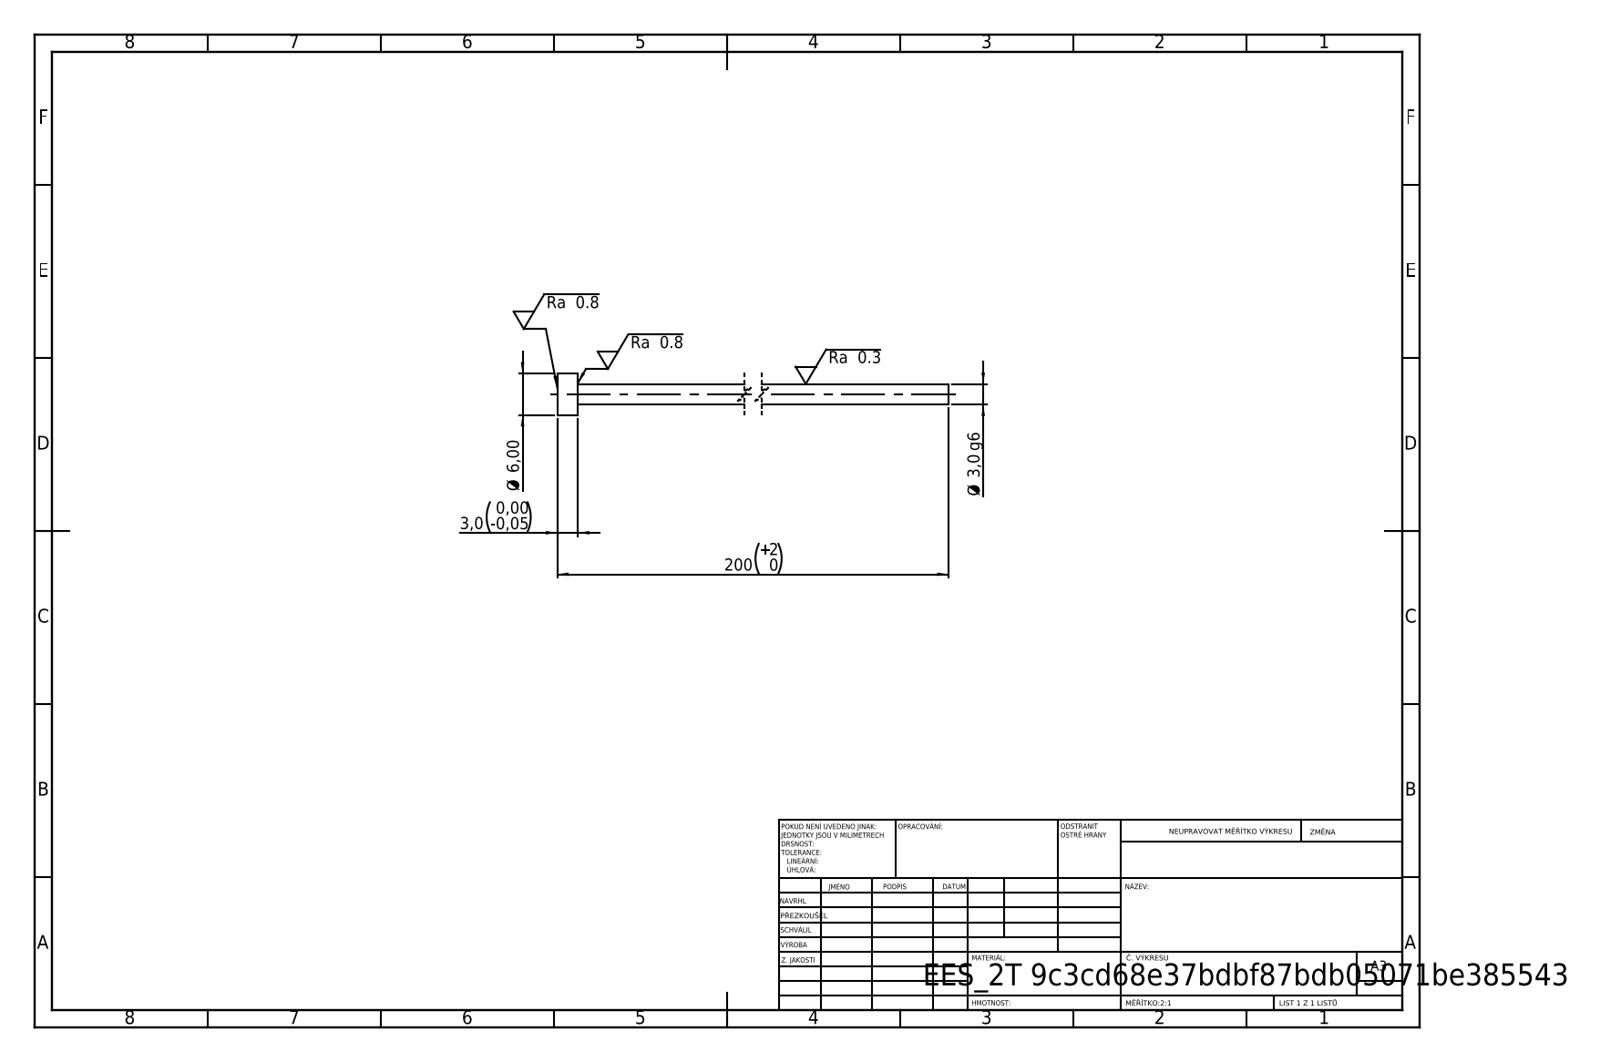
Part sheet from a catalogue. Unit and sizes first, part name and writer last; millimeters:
Units: millimetres
Overall size (bounding box): 200 × 6 × 6
Round bosses / shafts (diameter × count): ⌀6 ×1, ⌀3 ×1
Main face-to-face distances: 3, 200, 197
Volume: 1 477 mm³ · Surface area: 1 970 mm²
Bodies: 1 solid, 7 faces (3 planar, 4 cylindrical, 0 other)
STEP written by: SolidWorks 2019 (CONFIG_CONTROL_DESIGN)
